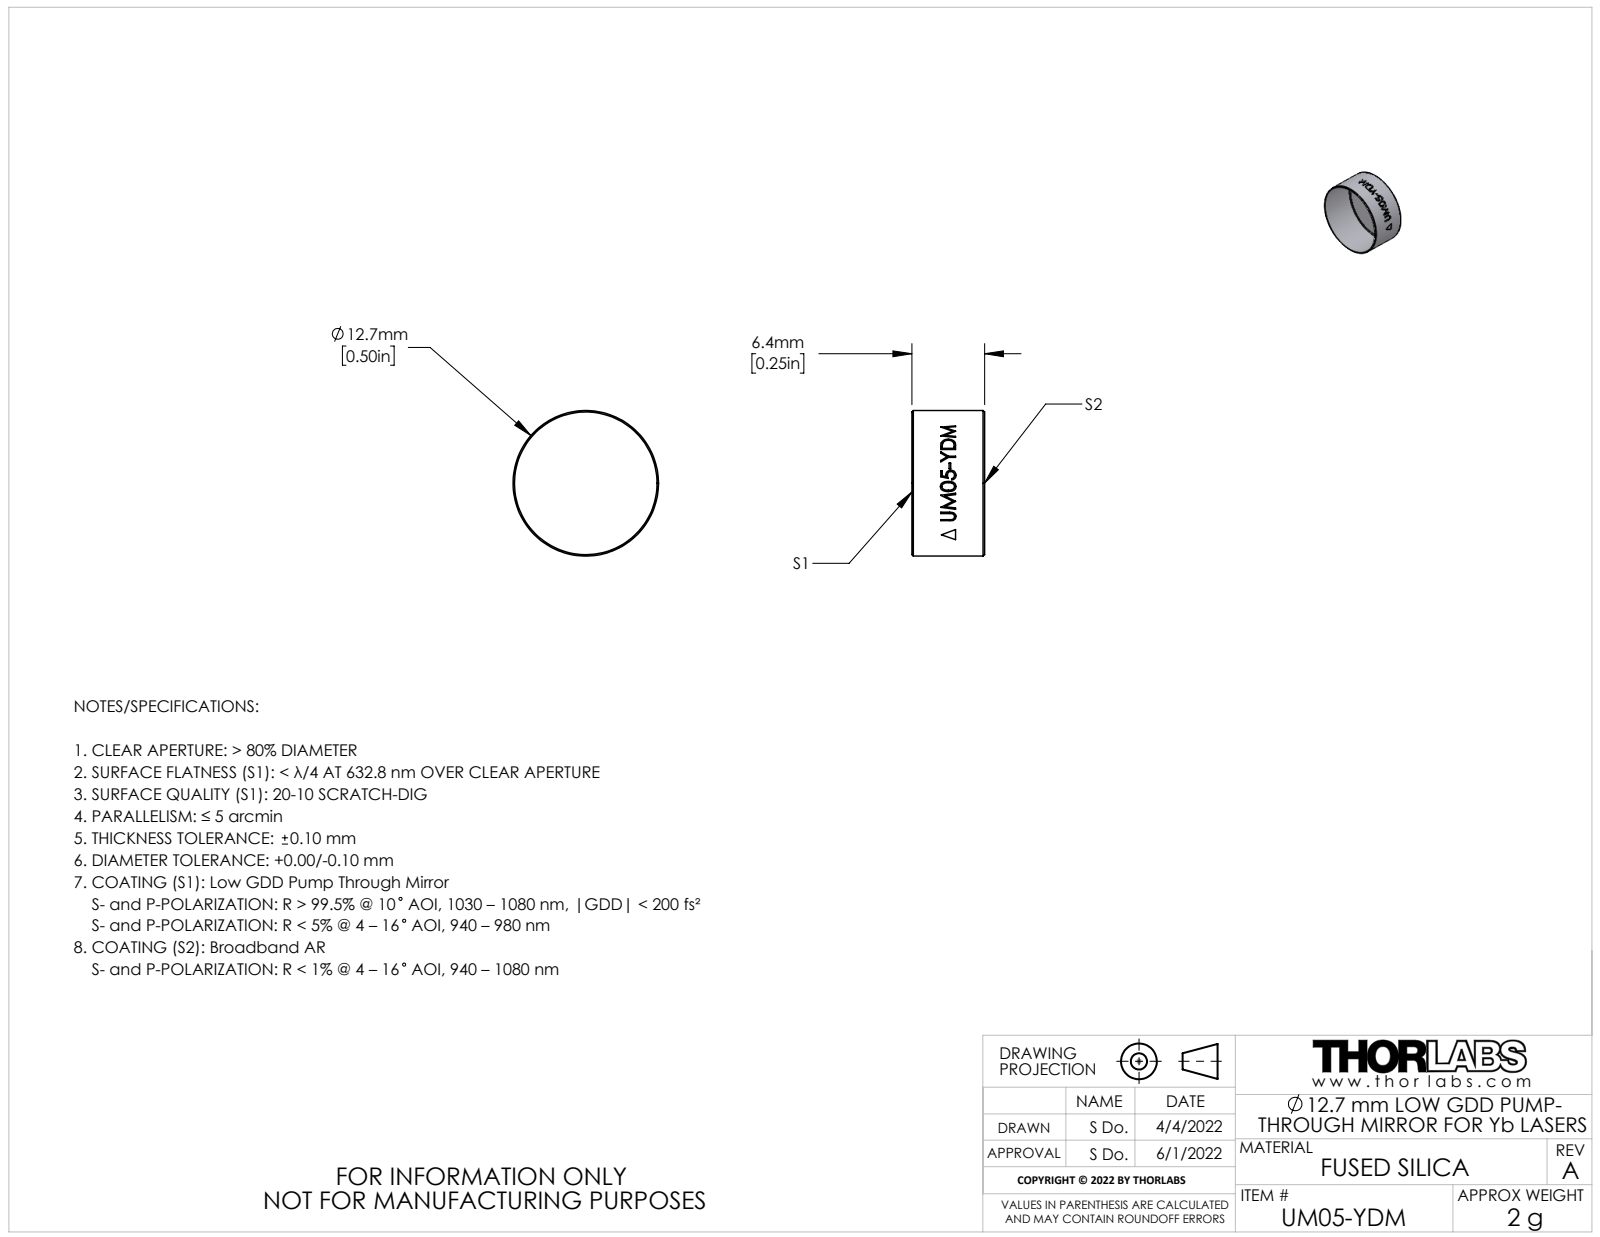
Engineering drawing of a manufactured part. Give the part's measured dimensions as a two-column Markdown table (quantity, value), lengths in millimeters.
| quantity | value |
| --- | --- |
| part name | TTN283370-E0W |
| STEP written by | SolidWorks 2018 (AUTOMOTIVE_DESIGN) |
| units | millimeters |
| bodies | 1 solid, 25 faces (2 planar, 19 cylindrical, 4 other) |
| overall size | 12.7 × 12.7 × 6.35 |
| volume | 804 mm³ |
| surface area | 501 mm² |
| round holes (diameter × count) | 12.45 × 1 |
| round bosses / shafts (diameter × count) | 12.7 × 1 |
| main face-to-face distances | 6.35 |
